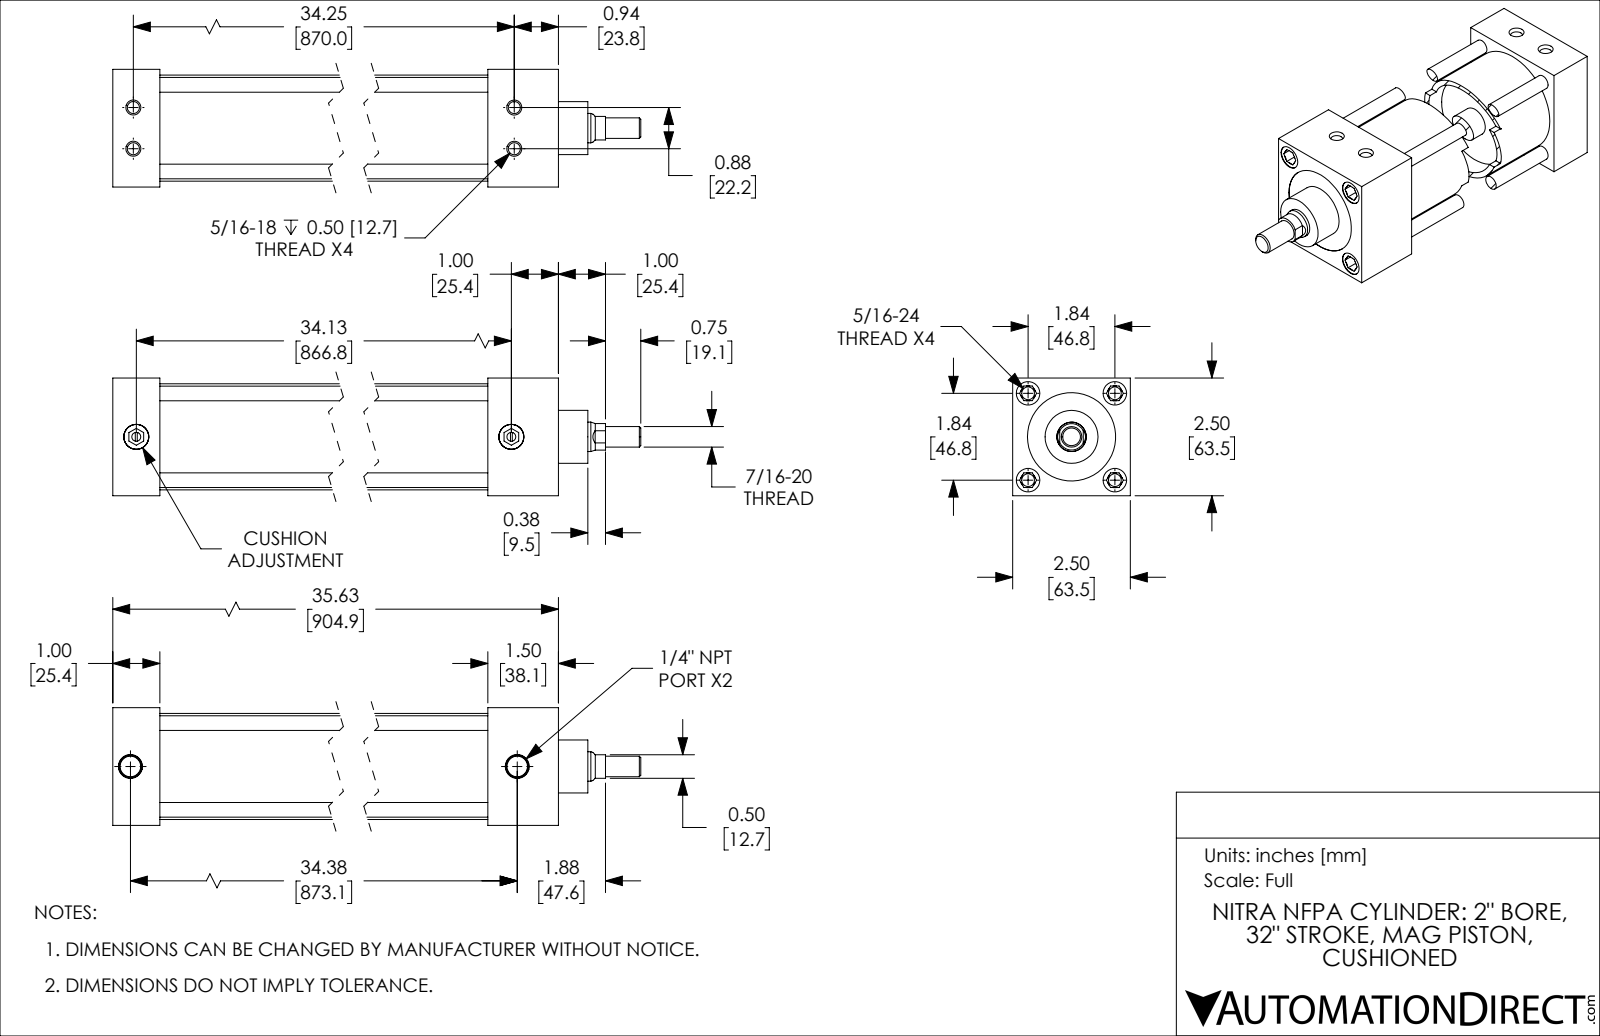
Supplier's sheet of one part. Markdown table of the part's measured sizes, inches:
| quantity | value |
| --- | --- |
| part name | D232320DT-MC_BODY; D232320DT-MC_PISTON_KK1; D232320DT-MC; D232320DT-MC_CUSHION |
| STEP written by | SolidWorks 2019 (CONFIG_CONTROL_DESIGN) |
| units | inches |
| bodies | 4 solids, 248 faces (90 planar, 78 cylindrical, 80 other) |
| overall size | 37.375 × 2.5 × 2.5 |
| volume | 66.71 in³ |
| surface area | 719.6 in² |
| round holes (diameter × count) | 0.272 × 7, 0.257 × 4, 0.5 × 4, 0.19 × 2, 0.438 × 2, 0.531 × 2, 0.626 × 1, 1.875 × 1, 2.001 × 1 |
| round bosses / shafts (diameter × count) | 0.312 × 4, 0.532 × 2, 2.251 × 1, 1.999 × 1, 1.125 × 1, 0.624 × 1, 0.437 × 1 |
| partial cylindrical surfaces (radius × count) | 0.281 × 1 |
| main face-to-face distances | 2.5, 1, 34.125, 33.125, 1.125, 2.125, 32, 35.625, 34.625, 33.5 |
| hole center spacings | 1.84, 1.844, 1.301, 0.441, 0.443, 0.875, 1.304, 2.602 |
